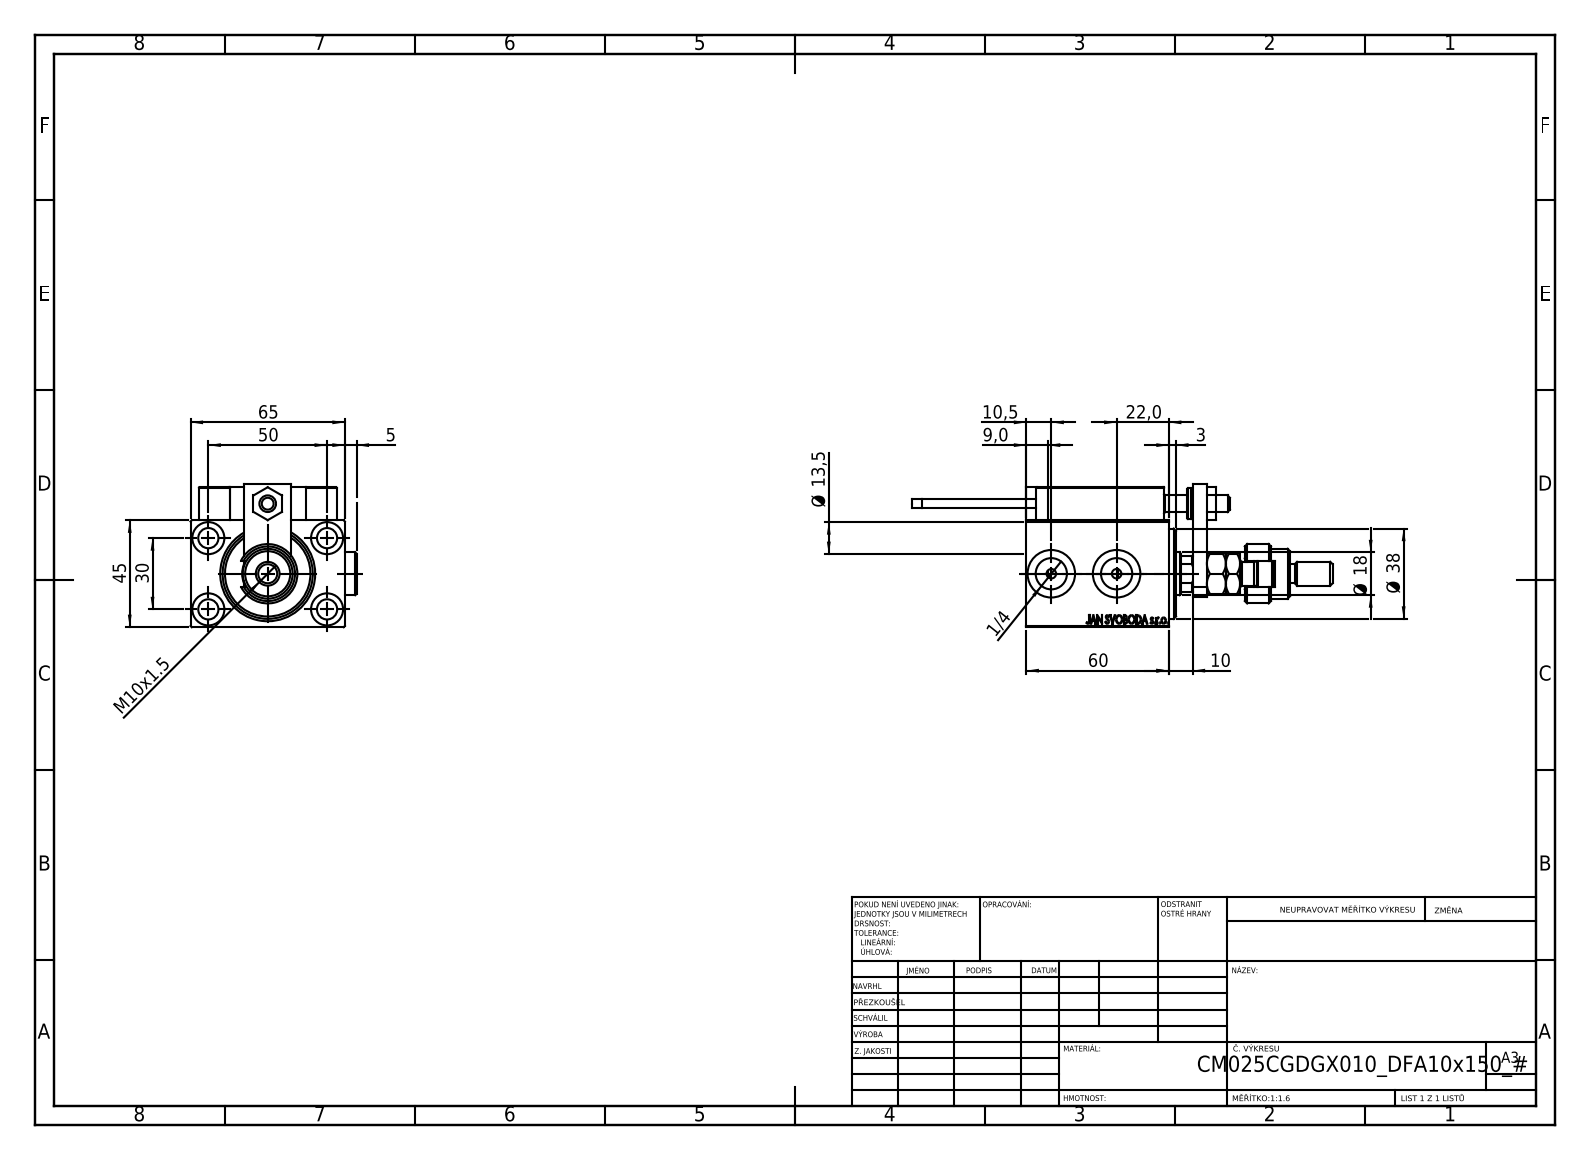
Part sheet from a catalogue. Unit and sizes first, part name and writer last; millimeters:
Units: millimetres
Overall size (bounding box): 177 × 69.9 × 60.5
Round holes (diameter × count): ⌀4 ×6, ⌀8 ×5, ⌀8.5 ×5, ⌀3.2 ×4, ⌀13.5 ×4, ⌀5 ×2, ⌀13.16 ×2, ⌀20 ×2, ⌀7 ×1, ⌀14.5 ×1, ⌀18 ×1, ⌀21.5 ×1
Round bosses / shafts (diameter × count): ⌀18 ×2, ⌀5 ×2, ⌀3.8 ×2, ⌀25 ×1, ⌀21 ×1, ⌀16 ×1, ⌀13 ×1, ⌀11 ×1
Partial cylindrical surfaces — rounded edges, fillets, slot ends (radius × count): R0.3 ×30, R3 ×2, R5.5 ×1, R8.5 ×1, R8.75 ×1
Main face-to-face distances: 45, 7, 14, 10, 5, 59, 3, 13, 6, 65
Hole centre spacings: 29.15, 11.37, 12.17, 20, 25.06, 28.9, 29.59, 29.69
Volume: 208 048 mm³ · Surface area: 73 455 mm²
Bodies: 27 solids, 1421 faces (624 planar, 215 cylindrical, 582 other)
Part name (STEP PRODUCT): ALLEN BOLT D5; ALLEN BOLT D8; KONCOVKA; SWITCH DIM B,W (+8 more)
STEP written by: SolidWorks 2019 (CONFIG_CONTROL_DESIGN)
